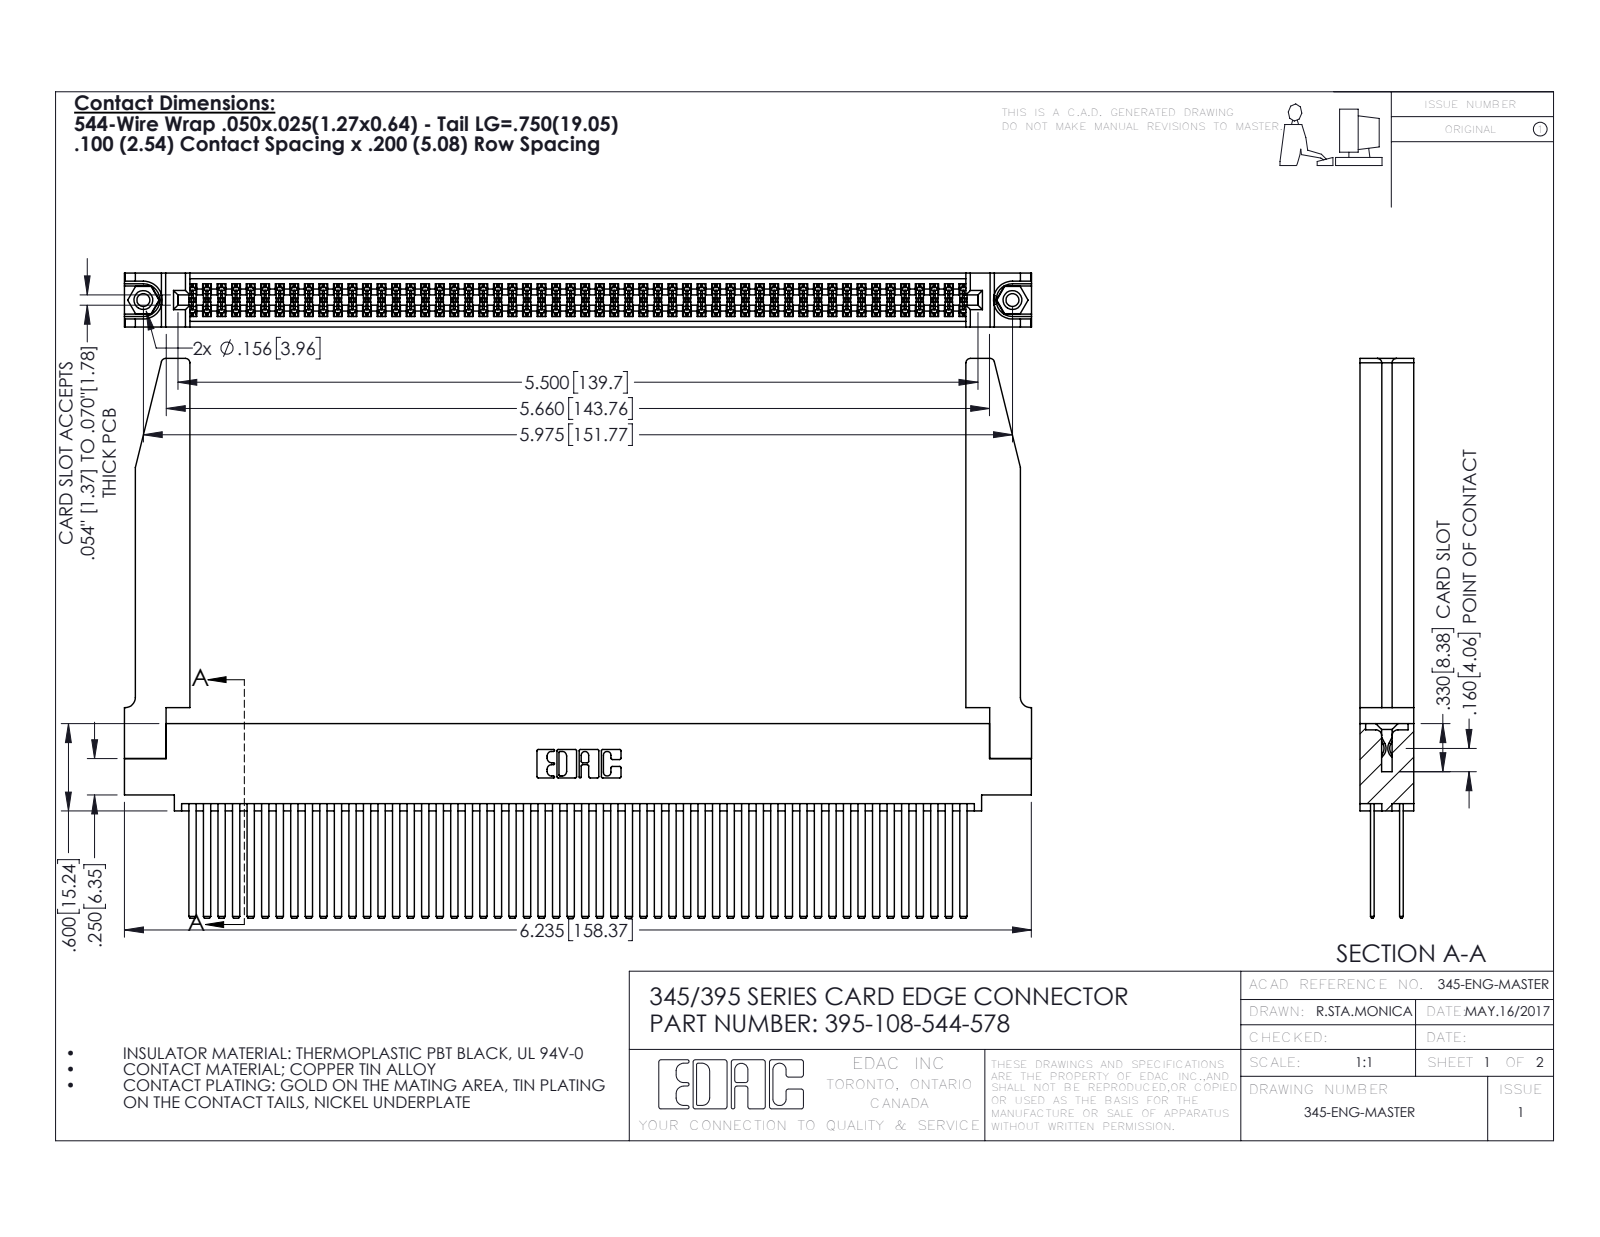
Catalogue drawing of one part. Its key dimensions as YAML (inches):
part_name: "345-292-001_345-293-144; 395-108-544-578; 345-250-001_345-250-001-102; 345-220-078_345-220-078 (+1 more)"
step_written_by: "SolidWorks 2016 (CONFIG_CONTROL_DESIGN)"
units: inches
bodies: {solids: 113, faces: 5116, planar: 3358, cylindrical: 1706, other: 52}
overall_size: [6.236, 3.847, 0.37]
volume: 1.508
surface_area: 56.79
round_holes:
  - {diameter: 0.089, count: 2}
  - {diameter: 0.125, count: 2}
  - {diameter: 0.156, count: 2}
  - {diameter: 0.064, count: 1}
round_bosses_or_shafts:
  - {diameter: 0.155, count: 2}
partial_cylinders:
  - {radius: 0.006, count: 162}
  - {radius: 0.01, count: 22}
  - {radius: 0.03, count: 8}
  - {radius: 0.007, count: 6}
  - {radius: 0.031, count: 6}
  - {radius: 0.026, count: 3}
  - {radius: 0.014, count: 2}
  - {radius: 0.019, count: 2}
face_to_face_distances: [0.072, 0.298, 0.098, 0.272, 0.025, 0.2, 0.37, 0.225, 0.175, 0.148]
hole_center_spacings: [0.27, 5.739, 5.975]
